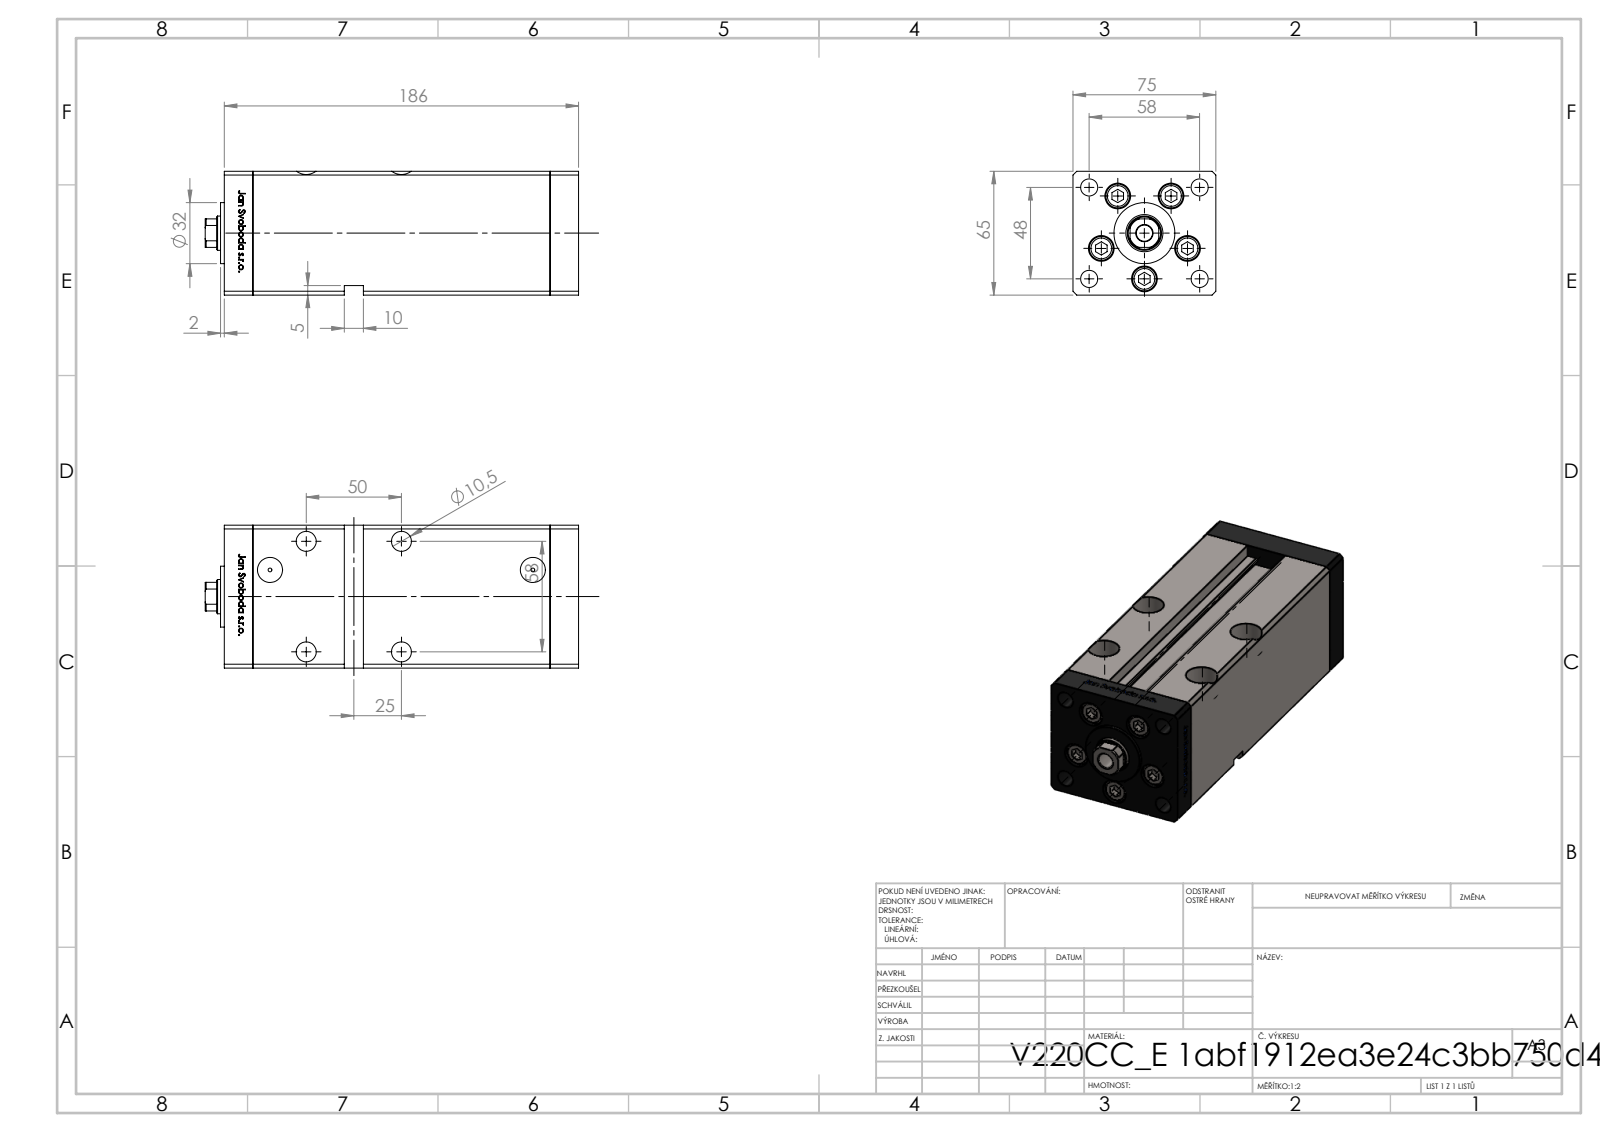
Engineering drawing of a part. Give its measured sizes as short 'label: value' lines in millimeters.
name: V220C BACK_E; V220C_E MIDDLE; ALLEN BOLT; V220C_VC_E (+1 more)
written by: SolidWorks 2019 (CONFIG_CONTROL_DESIGN)
unit: mm
bodies: 14 solids, 1212 faces (473 planar, 165 cylindrical, 574 other)
size: 196 × 75 × 65
volume: 769 603 mm³; area: 146 638 mm²
holes: 9× ⌀9, 5× ⌀13.5, 4× ⌀10.5, 4× ⌀16.5, 2× ⌀2, 2× ⌀13.16, 1× ⌀8.5, 1× ⌀18, 1× ⌀19.5
bosses: 5× ⌀12.5, 5× ⌀8, 1× ⌀32
rounds: 2× R0.93, 1× R8.5
face distances: 75, 65, 15, 156, 171, 186, 28, 54.5, 10.5, 26.25
hole spacings: 24, 37.64, 58, 15.67, 17.22, 27.71, 28.83, 29
